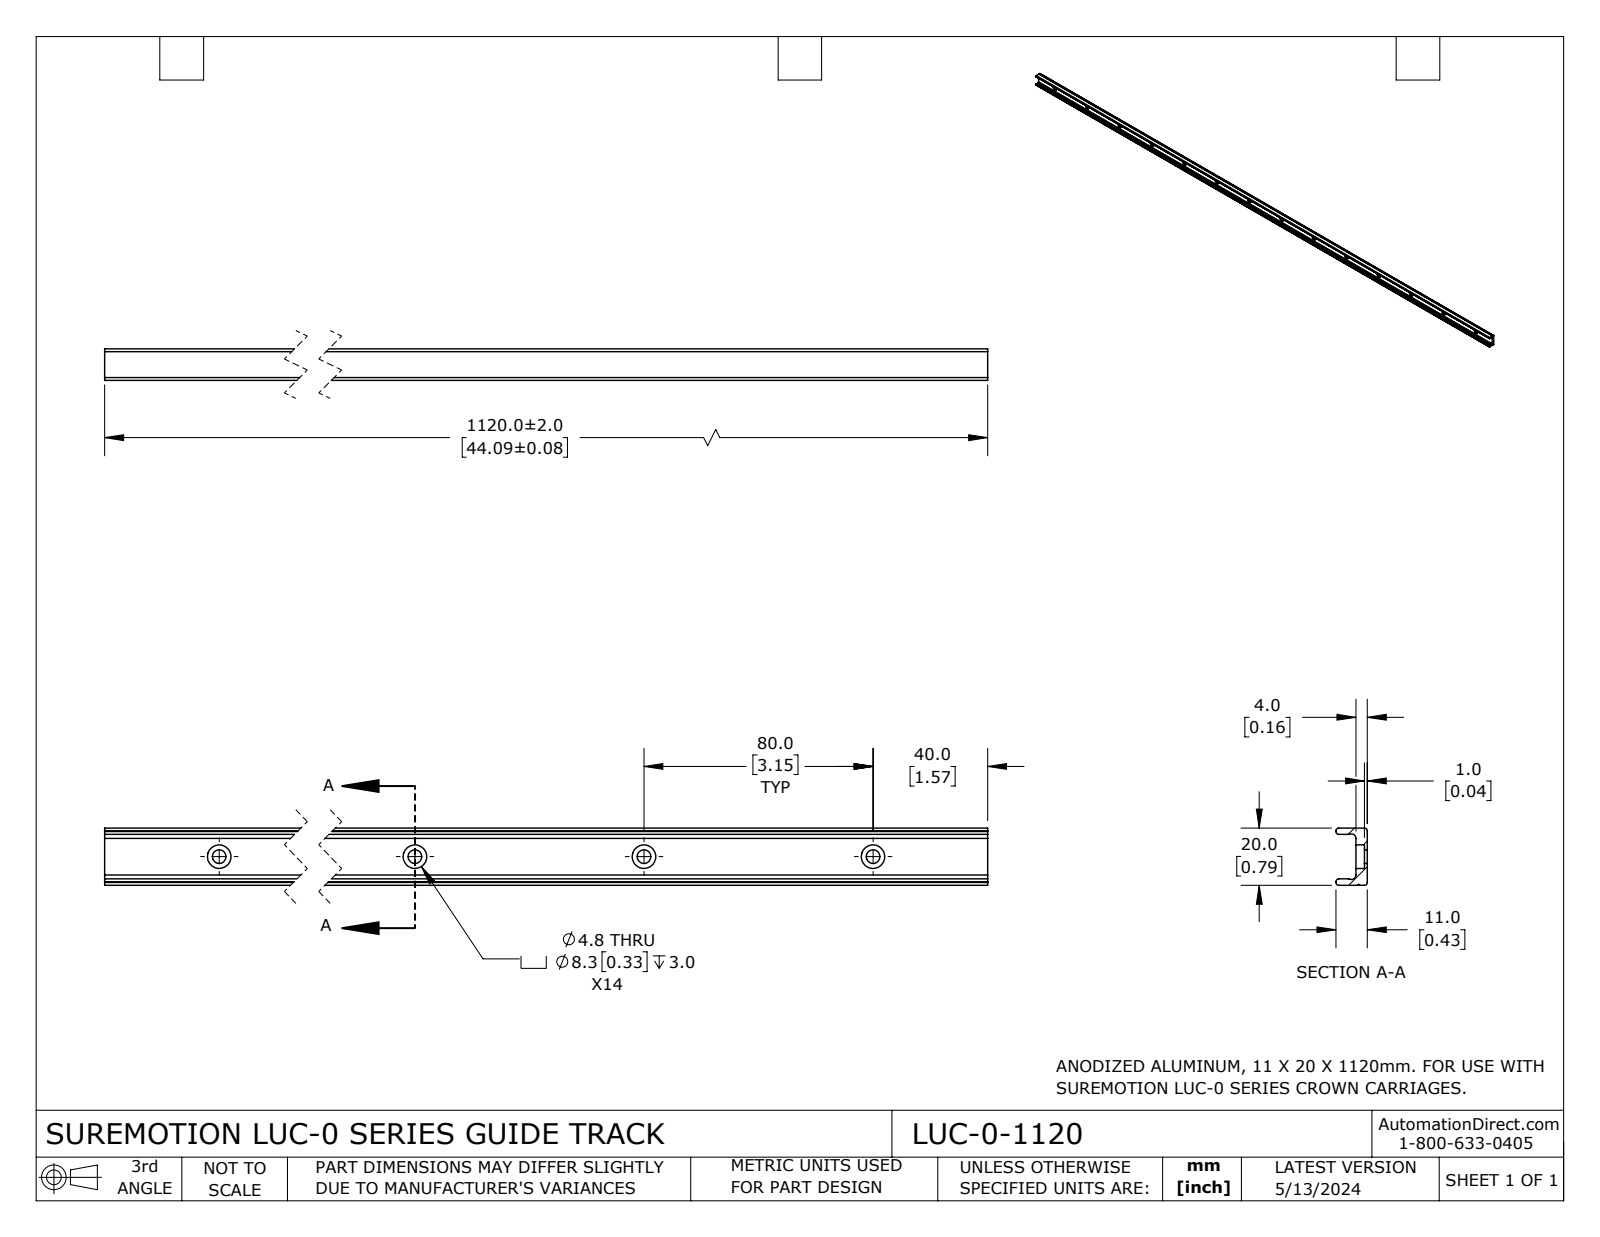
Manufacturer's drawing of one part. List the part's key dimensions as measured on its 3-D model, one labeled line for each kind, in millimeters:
Part name (STEP PRODUCT): LUC-0-1120
STEP written by: SolidWorks 2023 (CONFIG_CONTROL_DESIGN)
Units: millimetres
Bodies: 1 solid, 92 faces (25 planar, 67 cylindrical, 0 other)
Overall size (bounding box): 1120 × 19.99 × 11
Volume: 120 806 mm³ · Surface area: 82 612 mm²
Round holes (diameter × count): ⌀4.8 ×14, ⌀8.25 ×7, ⌀8.26 ×7
Partial cylindrical surfaces — rounded edges, fillets, slot ends (radius × count): R0.99 ×8, R1.6 ×2, R0.33 ×1
Main face-to-face distances: 4.01, 20, 2.23, 17.77, 15.54, 11, 6.99, 1.01, 3, 9.99
Hole centre spacings: 80, 160, 240, 320, 400, 480, 560, 640
